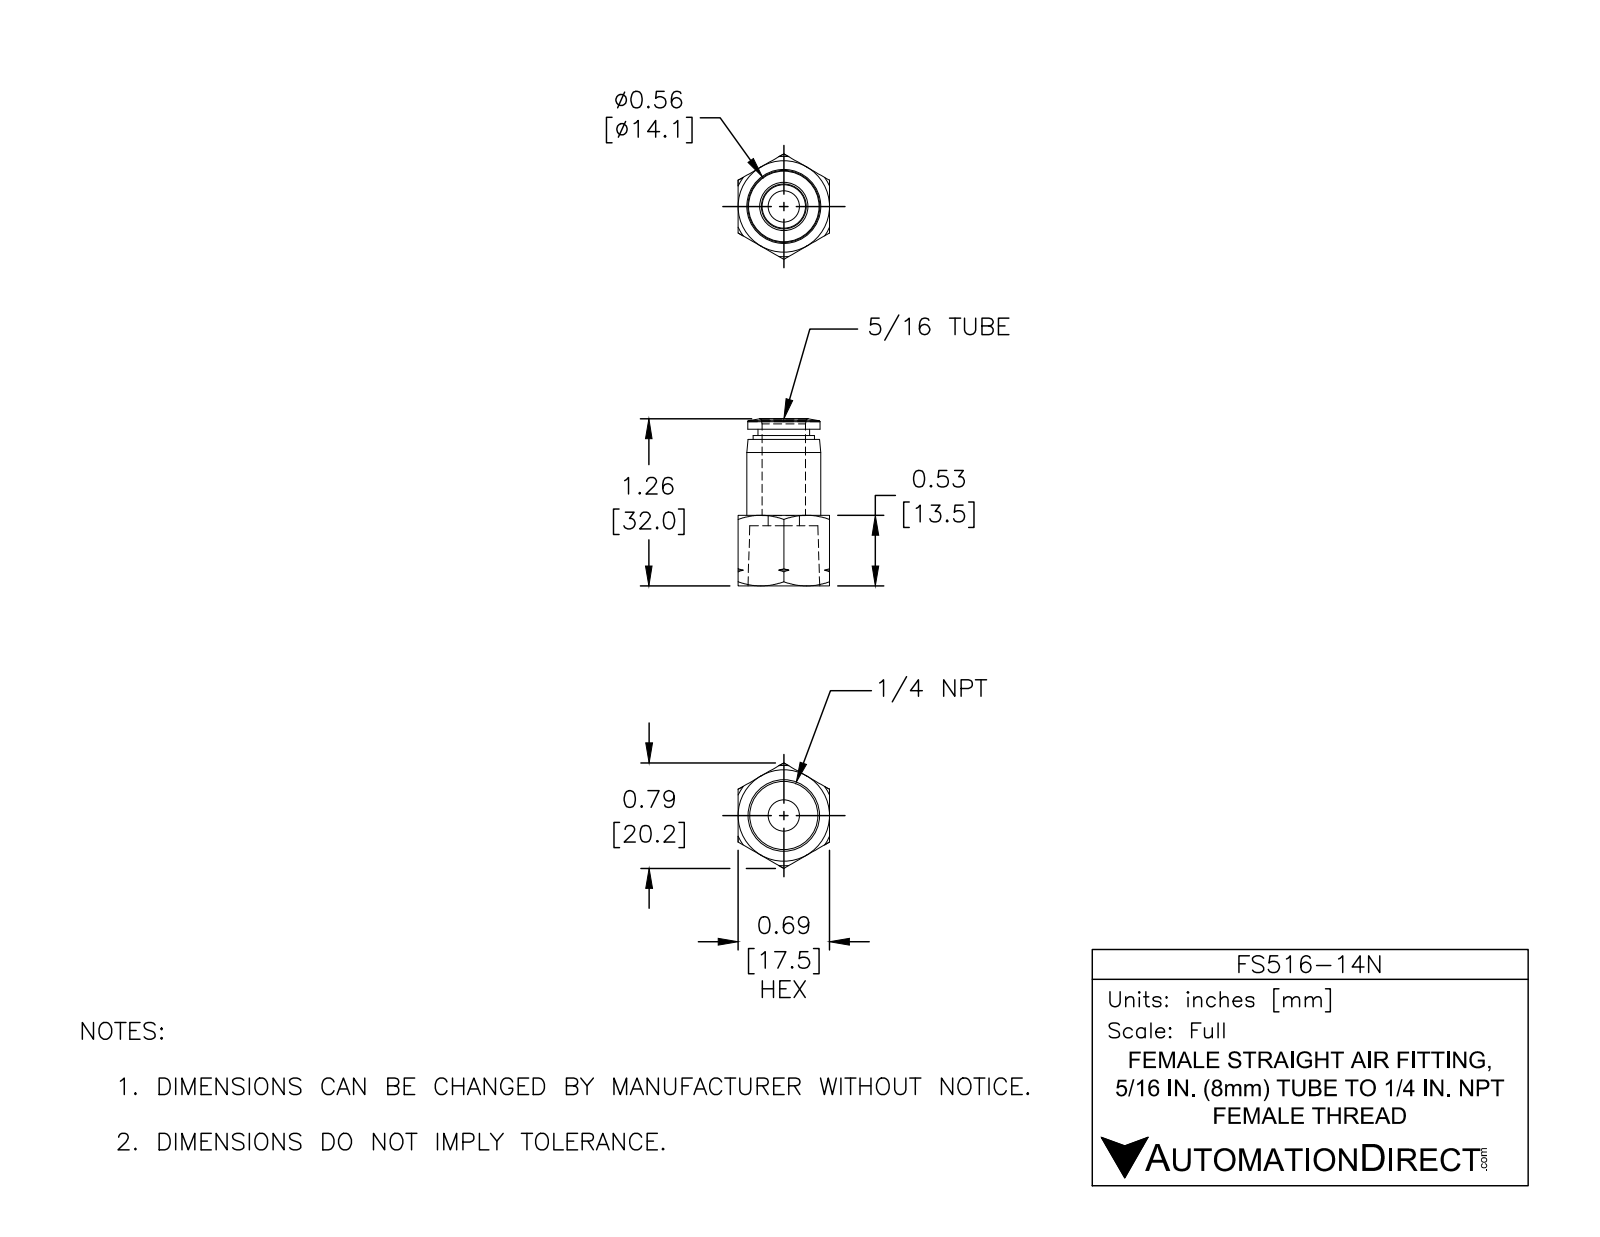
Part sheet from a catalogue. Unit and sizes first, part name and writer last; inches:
Units: inches
Overall size (bounding box): 1.258 × 0.794 × 0.687
Round holes (diameter × count): ⌀0.236 ×1, ⌀0.327 ×1
Round bosses / shafts (diameter × count): ⌀0.555 ×1, ⌀0.543 ×1, ⌀0.461 ×1, ⌀0.39 ×1
Main face-to-face distances: 0.687, 0.453, 0.531, 0.079, 1.179, 0.726, 0.648, 0.077, 0.65, 1.102
Volume: 0.219 in³ · Surface area: 4.894 in²
Bodies: 1 solid, 65 faces (13 planar, 12 cylindrical, 40 other)
Part name (STEP PRODUCT): FS516-14N
STEP written by: SolidWorks 2015 (CONFIG_CONTROL_DESIGN)
